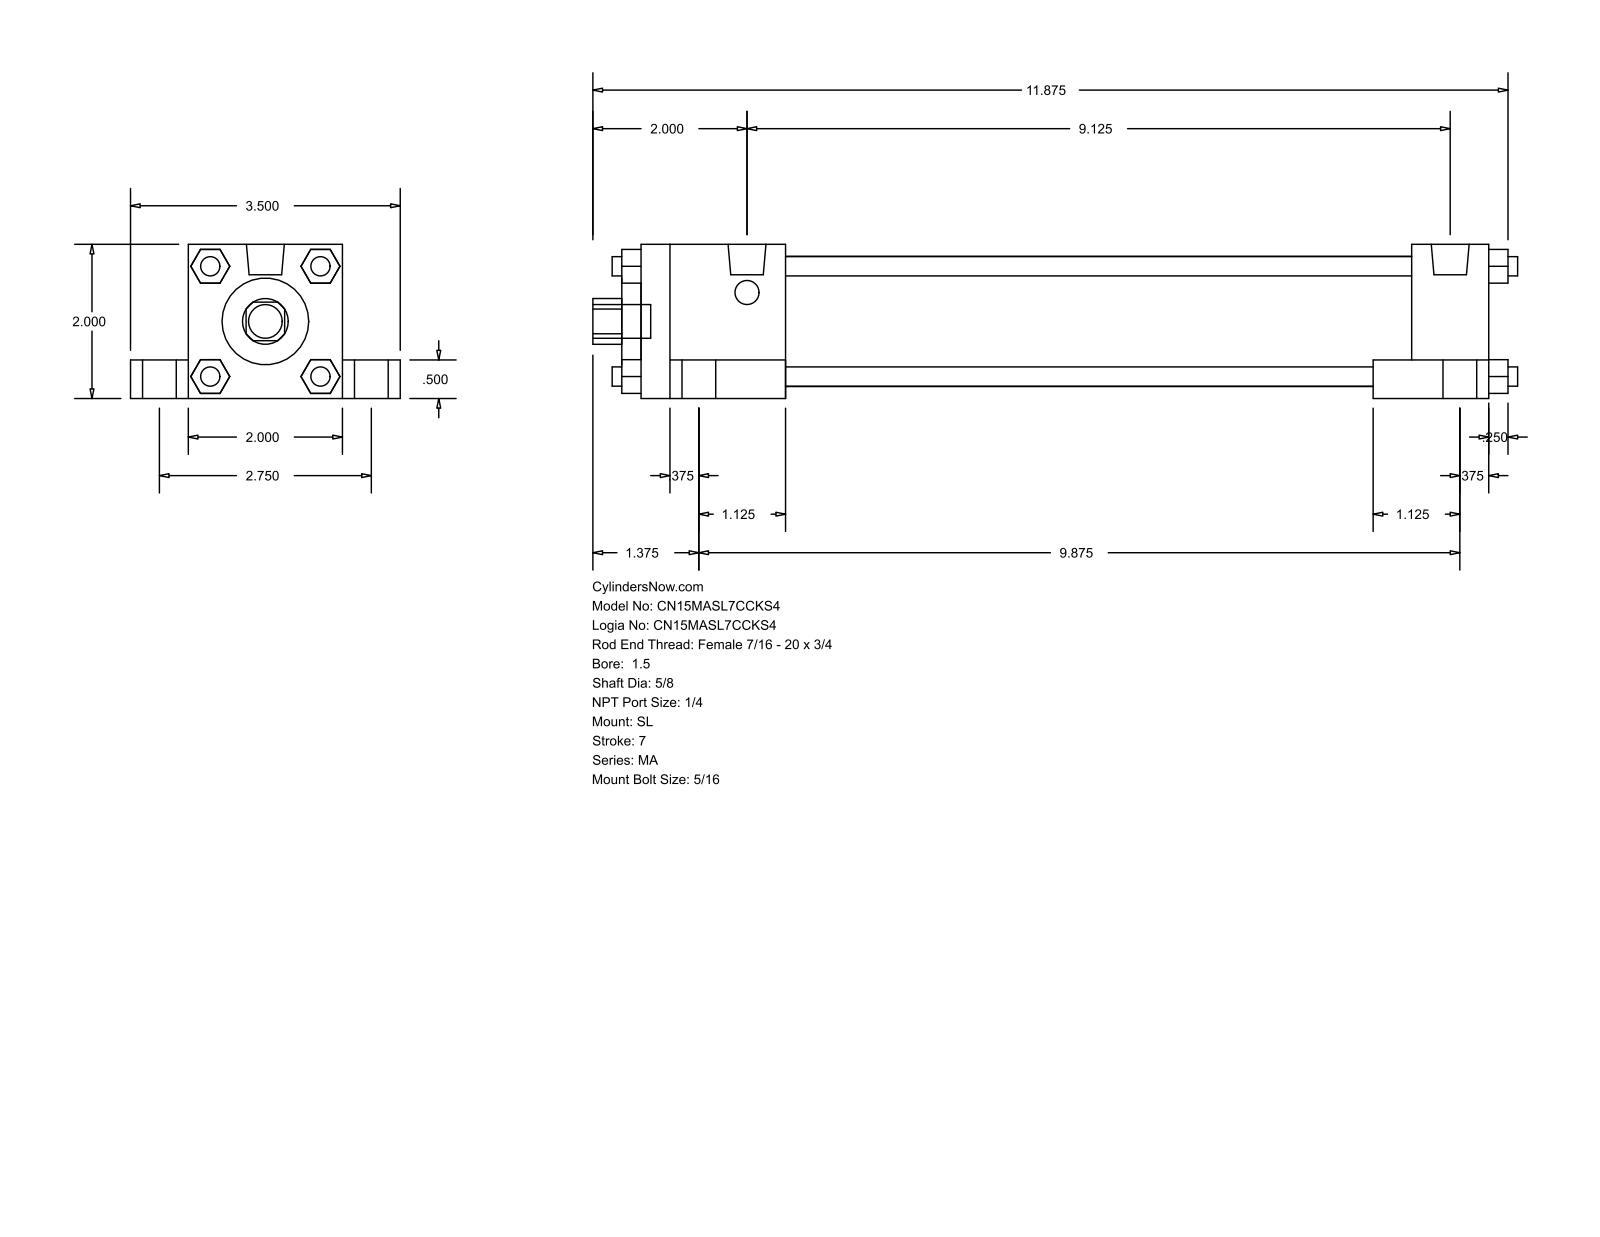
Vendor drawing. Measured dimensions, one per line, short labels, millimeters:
name: MA_SL__0150_0.625
written by: GSSL Pune (CONFIG_CONTROL_DESIGN)
unit: mm
bodies: 0 solids, 148 faces (112 planar, 36 cylindrical, 0 other)
size: 304.8 × 88.9 × 50.8
holes: 1× ⌀15.88, 1× ⌀28.57, 1× ⌀42.93
bosses: 5× ⌀11.11, 4× ⌀17.46, 4× ⌀7.94, 4× ⌀6.35, 2× ⌀12.49
rounds: 1× R7.54
face distances: 50.8, 19.05, 38.1, 12.7, 69.85, 279.39, 6.35, 9.52, 285.74, 254
